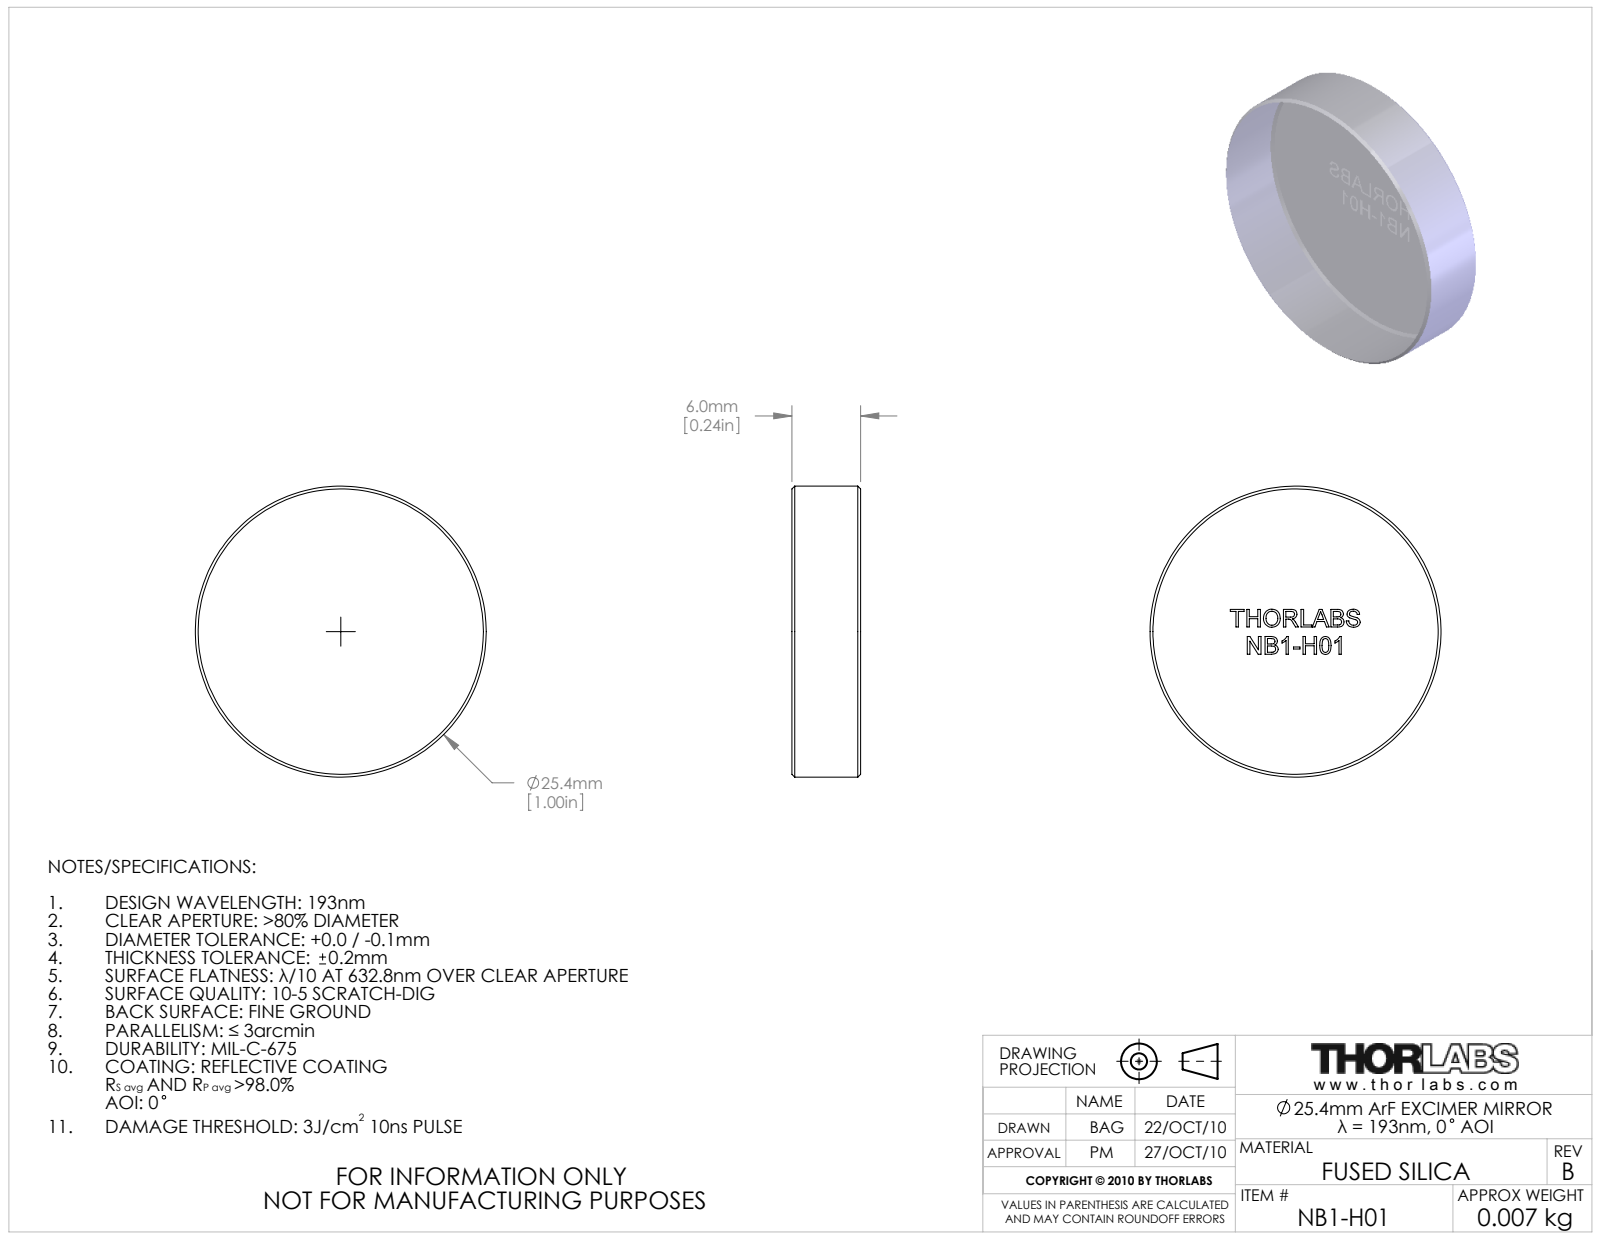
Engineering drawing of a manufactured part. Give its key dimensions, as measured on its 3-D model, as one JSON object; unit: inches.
{"part_name": "5383-E0W", "step_written_by": "SolidWorks 2009 (AUTOMOTIVE_DESIGN)", "units": "inches", "bodies": {"solids": 1, "faces": 201, "planar": 129, "cylindrical": 2, "other": 70}, "overall_size": [1, 1, 0.236], "volume_in3": 0.185, "surface_area_in2": 2.276, "round_bosses_or_shafts": [[1, 1]], "face_to_face_distances": [0.236, 0.061, 0.093, 0.193, 0.086, 0.038, 0.054, 0.094, 0.047, 0.146]}
